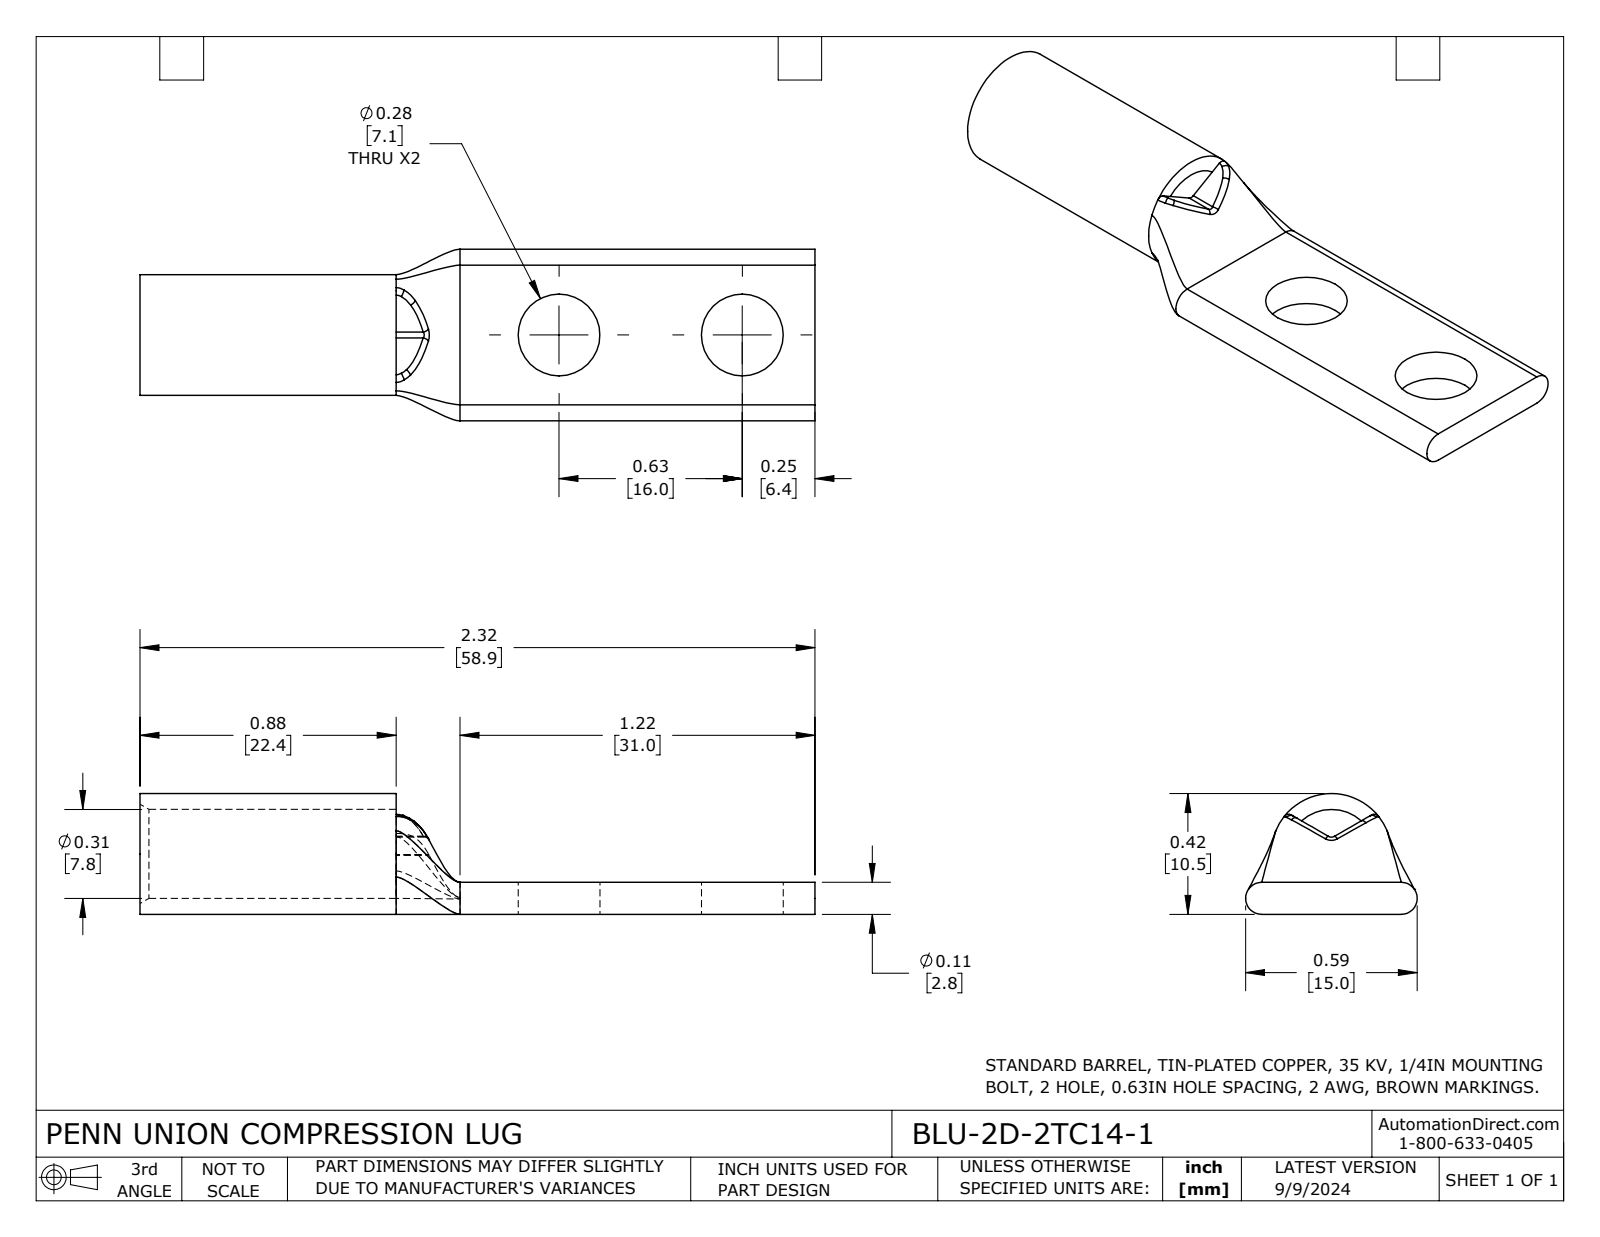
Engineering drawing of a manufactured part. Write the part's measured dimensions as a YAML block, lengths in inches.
part_name: "BLU-2D-2TC14-1"
step_written_by: "SolidWorks 2023 (CONFIG_CONTROL_DESIGN)"
units: inches
bodies: {solids: 1, faces: 41, planar: 11, cylindrical: 13, other: 17}
overall_size: [2.32, 0.59, 0.415]
volume: 0.129
surface_area: 4.256
round_holes:
  - {diameter: 0.281, count: 2}
  - {diameter: 0.306, count: 1}
round_bosses_or_shafts:
  - {diameter: 0.415, count: 1}
partial_cylinders:
  - {radius: 0.02, count: 2}
  - {radius: 0.055, count: 2}
face_to_face_distances: [0.11, 2.32, 0.88, 1.44, 0.054, 1.1, 0.22, 1.22]
hole_center_spacings: [0.63]
